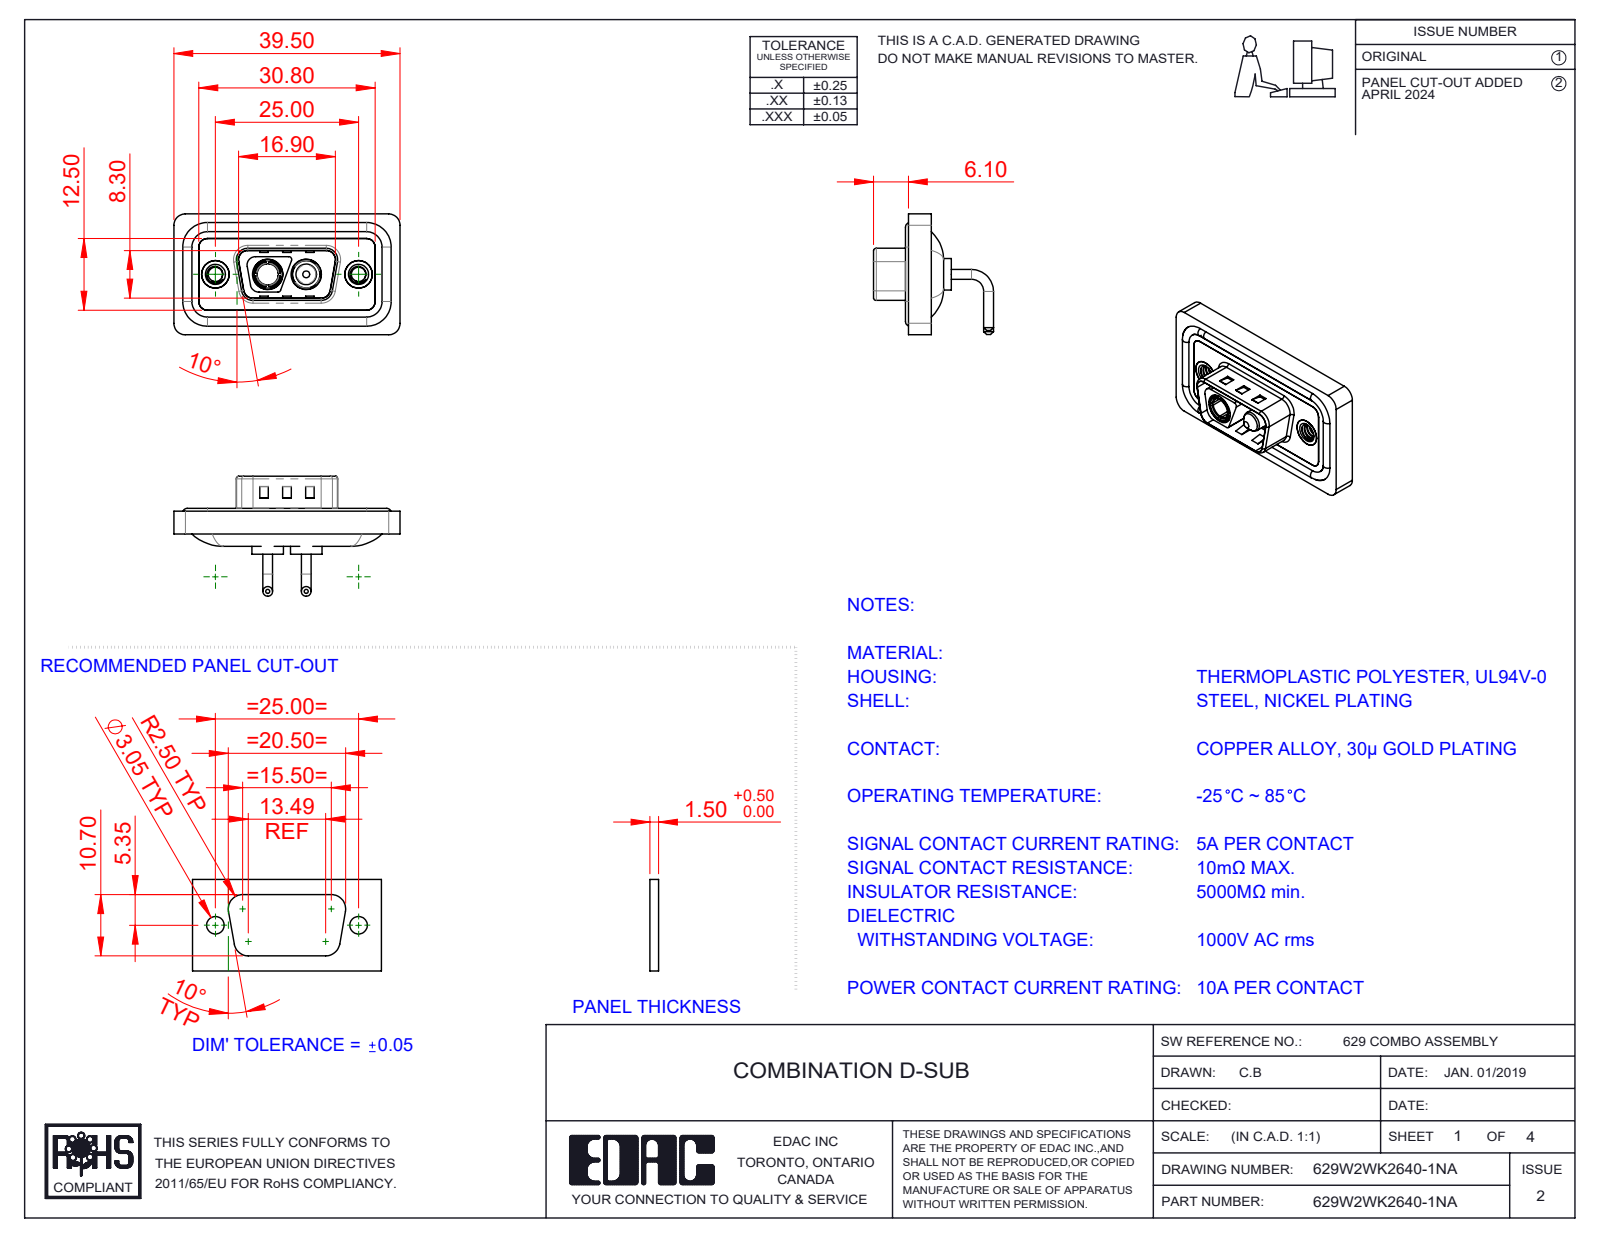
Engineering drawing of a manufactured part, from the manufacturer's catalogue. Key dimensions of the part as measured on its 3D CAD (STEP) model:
Part name (STEP PRODUCT): 629W2WK2640-1NA; 629Combo Waterproof Housing_09 Contacts; Power Pin_10A RA; 629Combo Shell Front_09 Contacts (+4 more)
STEP written by: SolidWorks 2023 (CONFIG_CONTROL_DESIGN)
Units: millimetres
Bodies: 11 solids, 536 faces (189 planar, 229 cylindrical, 118 other)
Overall size (bounding box): 39.5 × 21.1 × 20.95
Volume: 4 567 mm³ · Surface area: 7 431 mm²
Round holes (diameter × count): ⌀2.5 ×2, ⌀4 ×2, ⌀4.8 ×2, ⌀4.85 ×2, ⌀5 ×2, ⌀5.3 ×2, ⌀3.7 ×1
Round bosses / shafts (diameter × count): ⌀1.7 ×4, ⌀1.6 ×4, ⌀5.5 ×2, ⌀5.2 ×2, ⌀4.9 ×2, ⌀4.75 ×2, ⌀3.75 ×2, ⌀4.96 ×1
Partial cylindrical surfaces — rounded edges, fillets, slot ends (radius × count): R1.5 ×20, R2 ×18, R0.5 ×10, R1.6 ×8, R0.25 ×4, R0.6 ×4, R0.65 ×4, R0.9 ×4
Main face-to-face distances: 0.4, 2.9, 1.1, 0.8, 2.1, 2.5, 3.1, 1.6, 4.5, 1.5
Hole centre spacings: 9.14, 15.86, 6.72, 25
